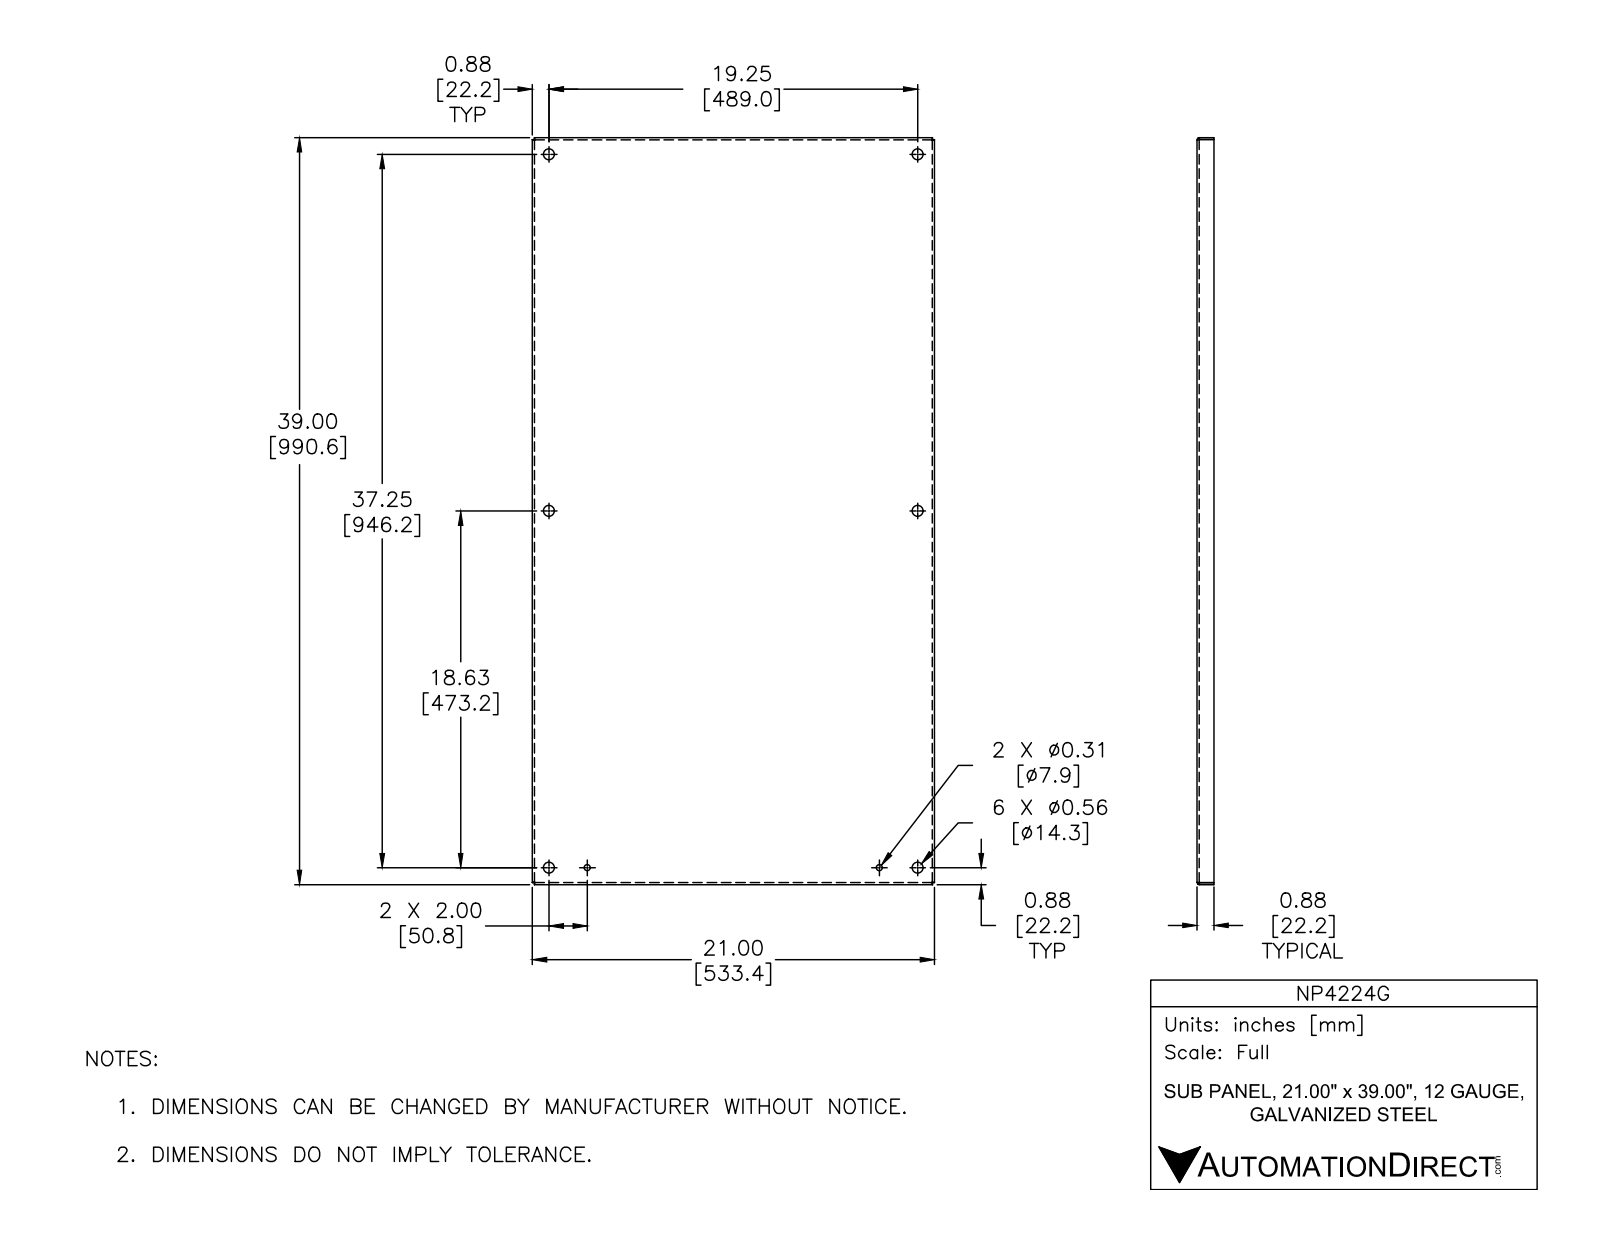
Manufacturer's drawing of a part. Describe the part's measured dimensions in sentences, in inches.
The part is named "NP4224G". Its 3-D file was written by "Autodesk Inventor 2012 (AUTOMOTIVE_DESIGN)". It is 1 solid with 46 faces: 22 planar, 16 cylindrical and 8 other. Overall it measures 39 by 21 by 0.875 inches. Its volume is 84.93 cubic inches and its surface area 1 826 square inches. Round holes: 6 of diameter 0.563, 2 of diameter 0.312. Partial cylindrical surfaces (rounded edges, fillets, slot ends): 4 of radius 0.031, 4 of radius 0.125. The main face-to-face distances are 0.094, 20.906, 38.906, 21, 20.813, 39, 38.813, 0.781, 0.875, 0.105. The hole center spacings are 18.625, 18.732, 19.25, 26.785, 26.786, 37.25, 37.304, 41.93.
